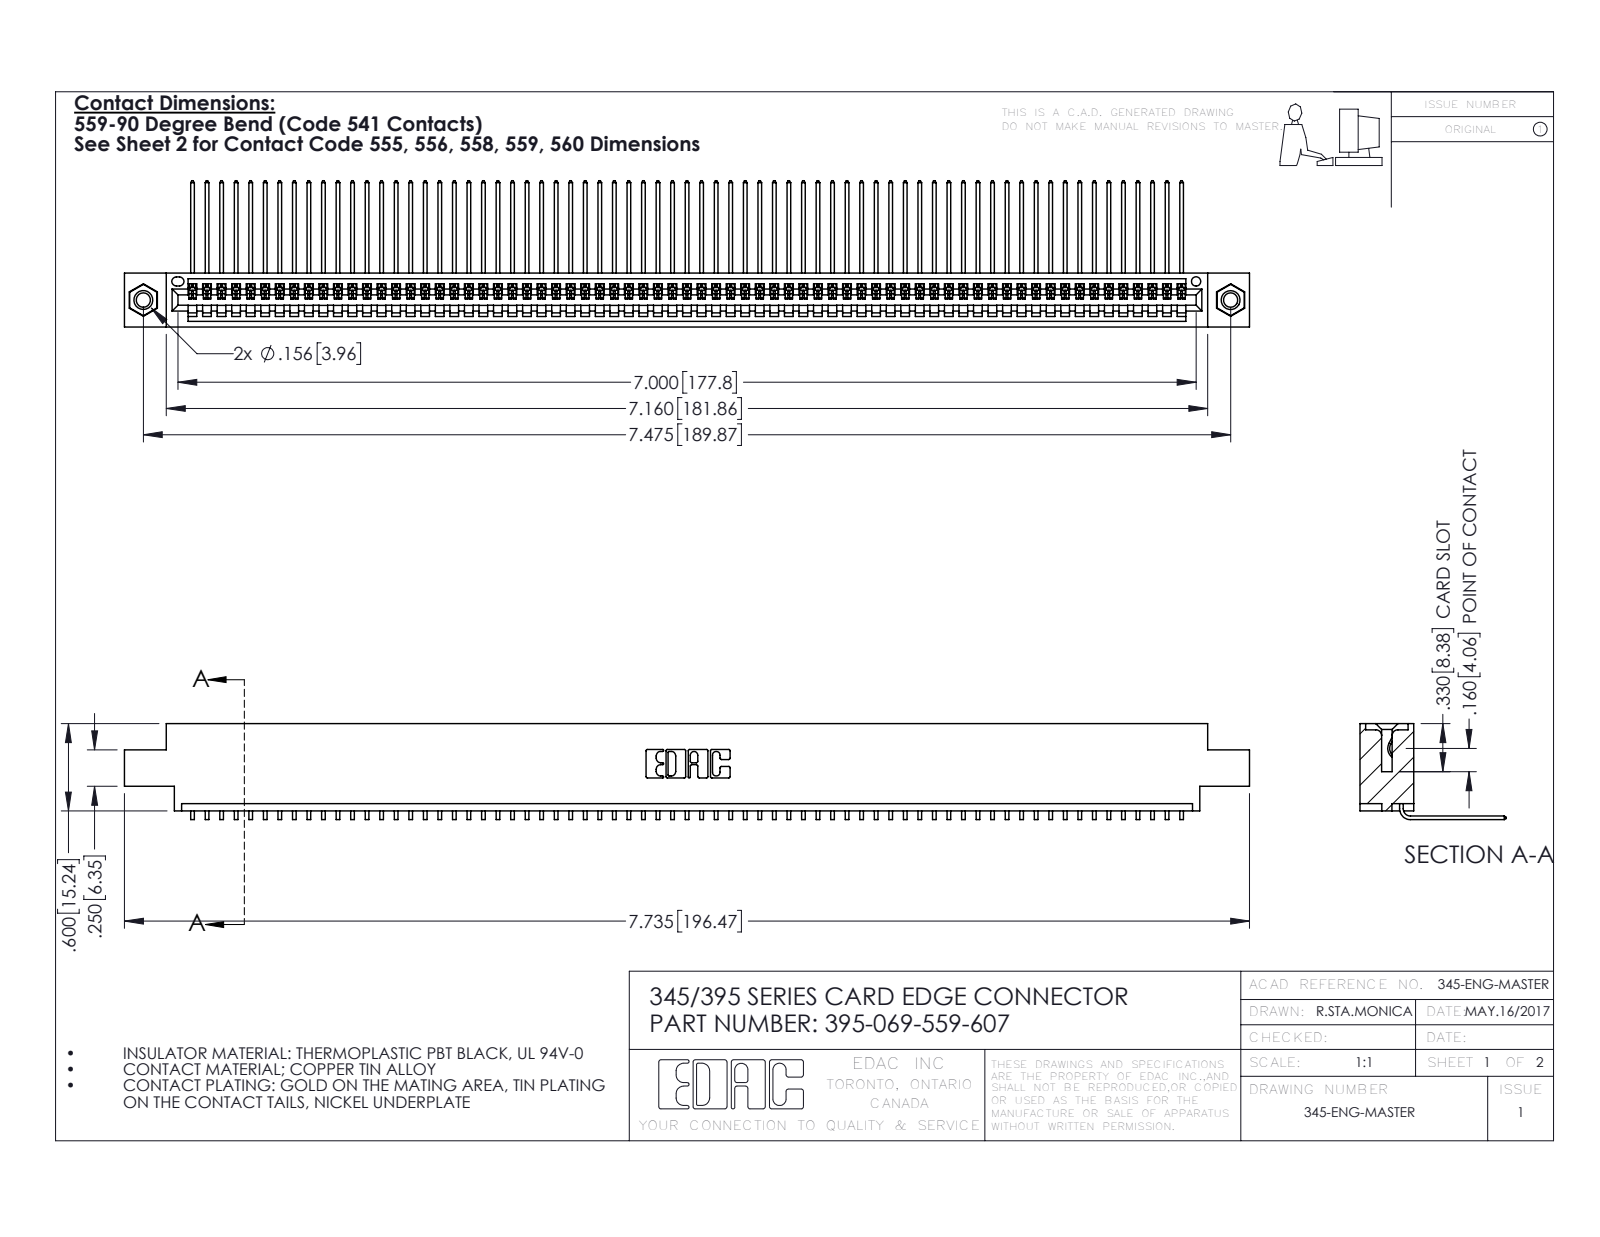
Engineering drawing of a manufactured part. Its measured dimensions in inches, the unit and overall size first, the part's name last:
Units: inches
Overall size (bounding box): 7.735 × 1.005 × 0.659
Round holes (diameter × count): ⌀0.098 ×2, ⌀0.125 ×2, ⌀0.156 ×2, ⌀0.064 ×1
Round bosses / shafts (diameter × count): ⌀0.155 ×2
Partial cylindrical surfaces — rounded edges, fillets, slot ends (radius × count): R0.006 ×138, R0.01 ×22, R0.007 ×6, R0.031 ×6, R0.026 ×3, R0.031 ×2, R0.04 ×2, R0.014 ×1
Main face-to-face distances: 0.072, 0.298, 0.37, 0.2, 0.098, 0.272, 0.025, 0.225, 0.175, 0.149
Hole centre spacings: 0.27, 7.239, 7.475
Volume: 1.159 in³ · Surface area: 42.01 in²
Bodies: 72 solids, 4330 faces (3014 planar, 1300 cylindrical, 16 other)
Part name (STEP PRODUCT): 345 Part_0.170 Offset - 0.156 Dia-TI; 345-250-001_345-250-005-103; 345-292-001_558 559 Tail - 1; 395-069-559-607
STEP written by: SolidWorks 2016 (CONFIG_CONTROL_DESIGN)
